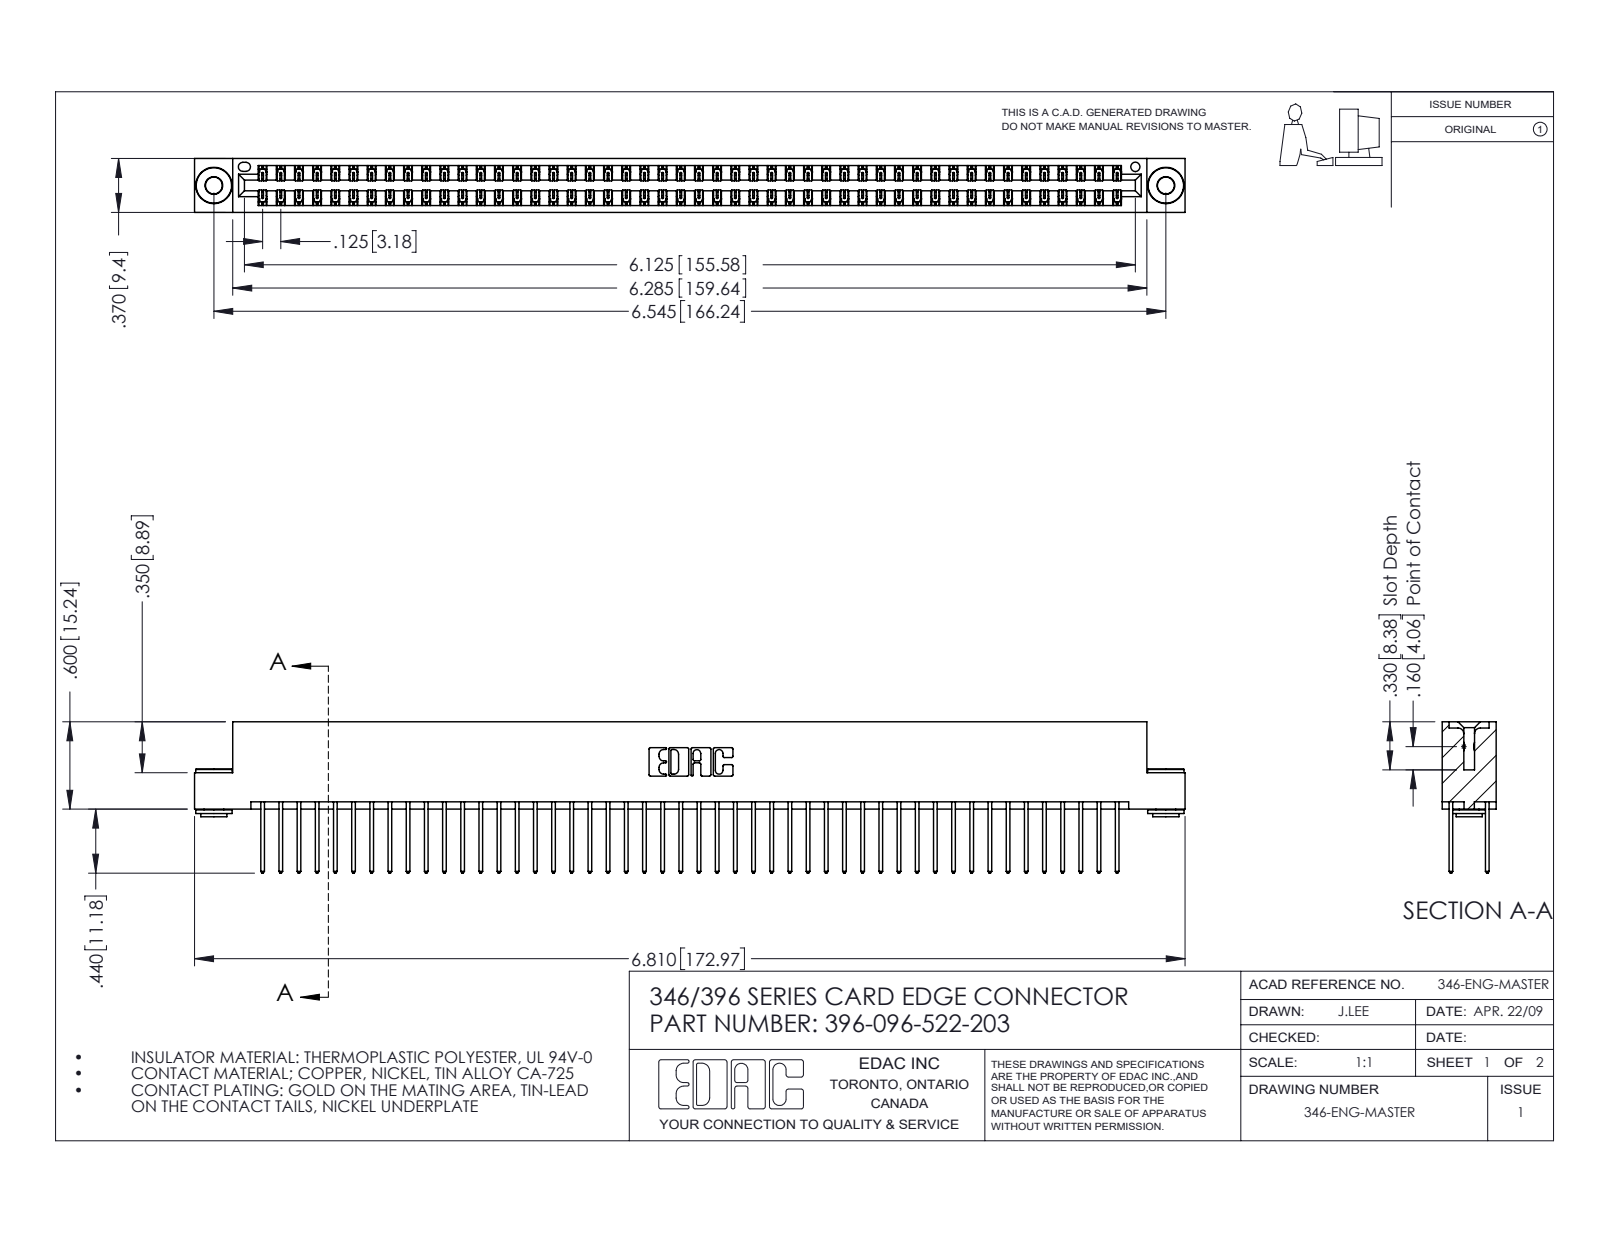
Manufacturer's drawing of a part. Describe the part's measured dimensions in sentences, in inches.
The part is named "346 Part_Flush Mounting Lugs - 0.156 Dia-TH; 396-096-522-203; 345-250-002_345-250-002-102; 345-292-001_345-293-122". Its 3-D file was written by "SolidWorks 2016 (CONFIG_CONTROL_DESIGN)". It is 99 solids with 5152 faces: 3446 planar, 1698 cylindrical and 8 other. Overall it measures 6.81 by 1.04 by 0.37 inches. Its volume is 1.048 cubic inches and its surface area 38.85 square inches. Round holes: 2 of diameter 0.116, 2 of diameter 0.156, 1 of diameter 0.064. Round bosses or shafts: 2 of diameter 0.25, 2 of diameter 0.18, 2 of diameter 0.136. Partial cylindrical surfaces (rounded edges, fillets, slot ends): 144 of radius 0.006, 96 of radius 0.01, 22 of radius 0.01, 6 of radius 0.007, 6 of radius 0.031, 3 of radius 0.026, 2 of radius 0.014, 2 of radius 0.022. The main face-to-face distances are 0.048, 0.322, 0.25, 0.025, 0.072, 0.298, 0.37, 0.275, 0.148, 0.222. The hole center spacings are 0.246, 6.336, 6.545.
